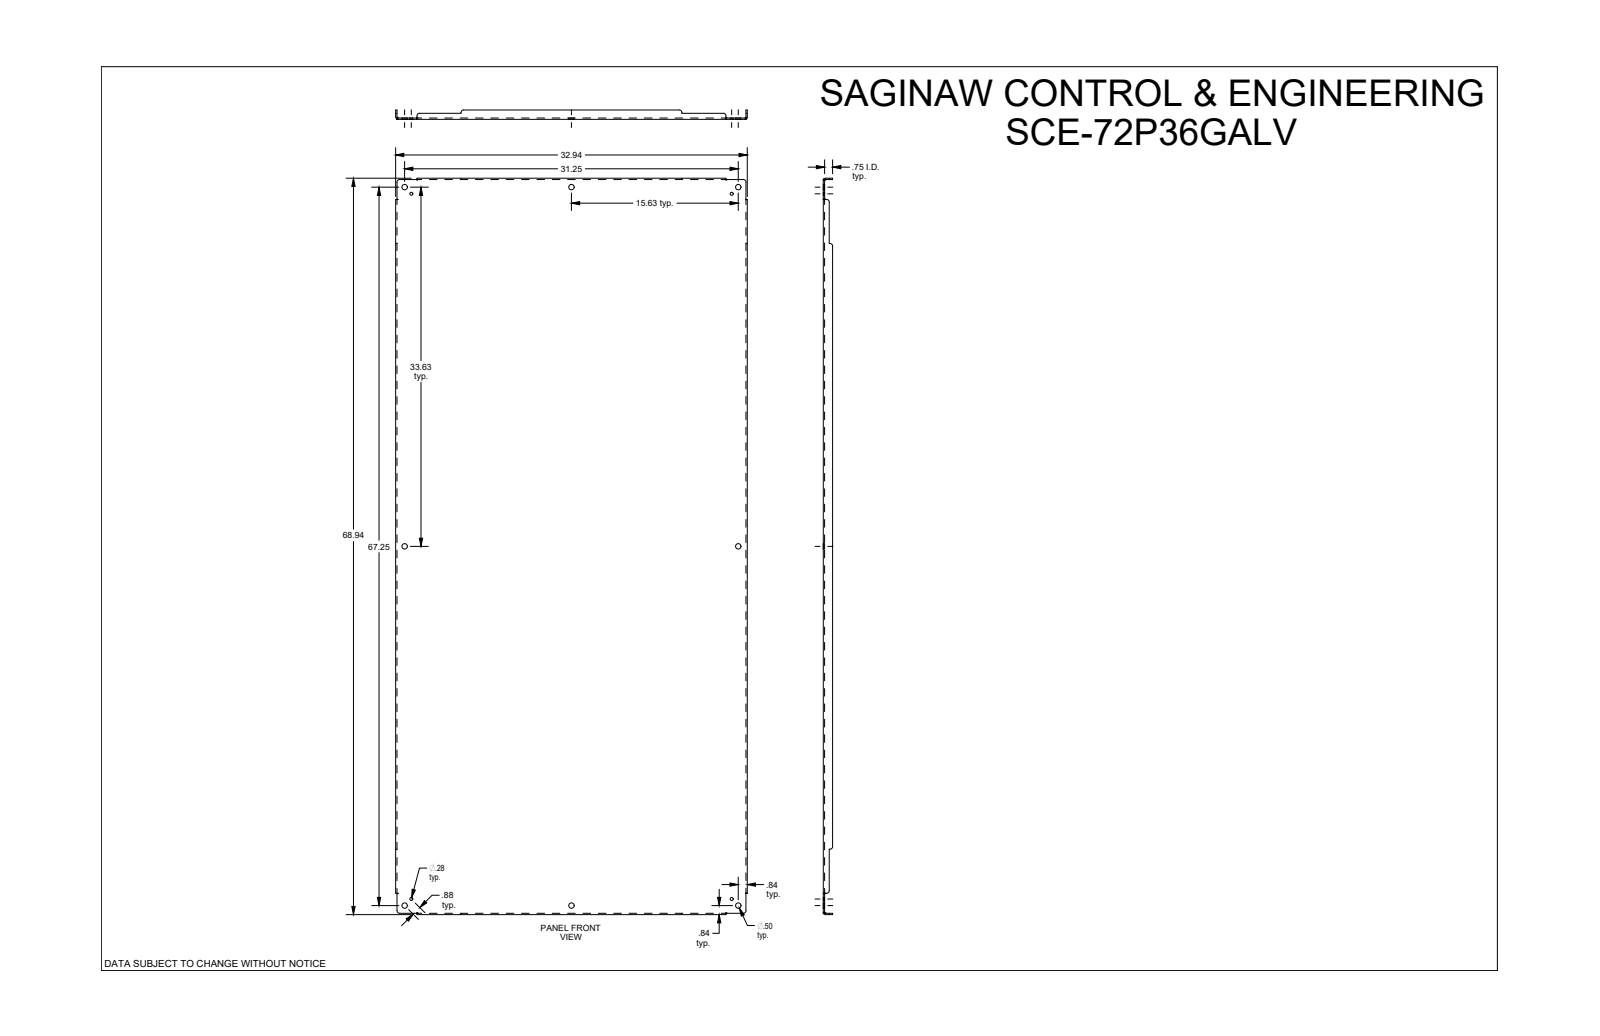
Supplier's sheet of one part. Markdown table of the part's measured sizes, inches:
| quantity | value |
| --- | --- |
| part name | SCE-72P36GALV |
| STEP written by | SolidWorks 2019 (CONFIG_CONTROL_DESIGN) |
| units | inches |
| bodies | 1 solid, 110 faces (46 planar, 40 cylindrical, 24 other) |
| overall size | 68.938 × 32.938 × 0.875 |
| volume | 297.9 in³ |
| surface area | 4 794 in² |
| round holes (diameter × count) | 0.5 × 8, 0.281 × 4 |
| partial cylindrical surfaces (radius × count) | 0.25 × 12, 0.112 × 4, 0.237 × 4 |
| main face-to-face distances | 0.125, 0.125, 32.813, 32.687, 32.938, 68.813, 0.75, 0.875, 68.687, 68.938 |
| hole center spacings | 0.875, 15.019, 15.625, 30.638, 33.012, 33.625, 37.078, 45.03 |
